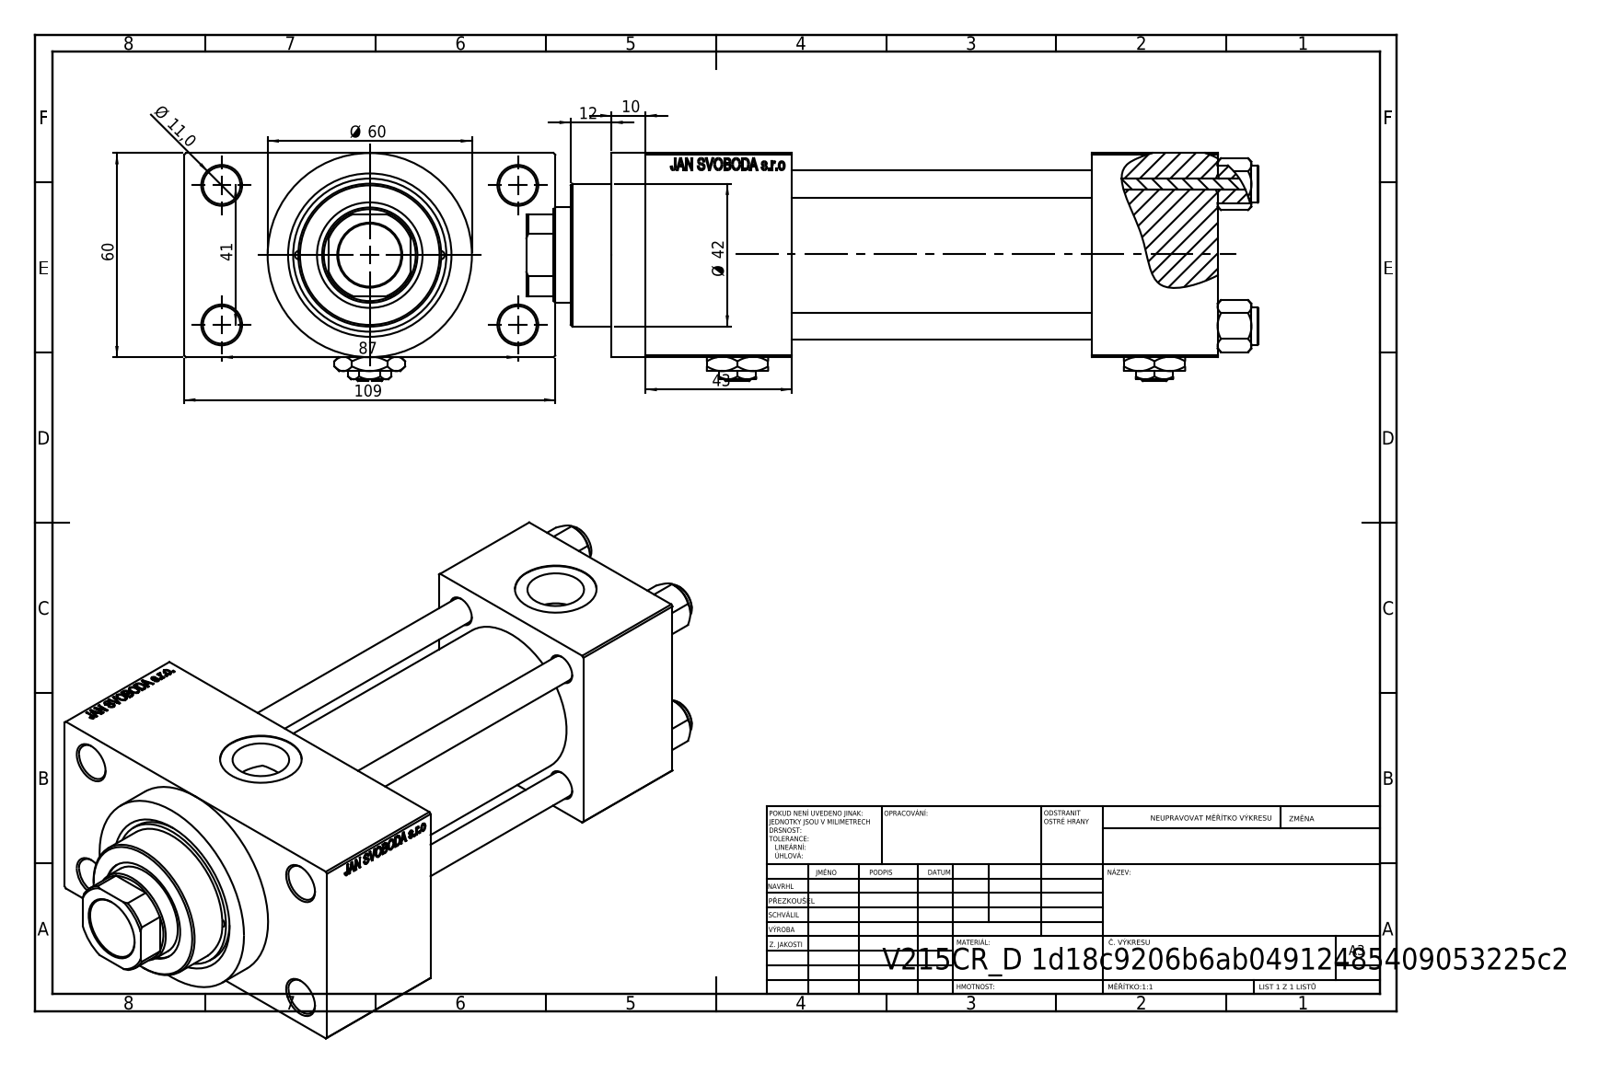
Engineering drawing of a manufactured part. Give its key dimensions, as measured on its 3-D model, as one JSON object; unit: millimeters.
{"part_name": "NUT_M5_D; V215CR_VCP_D; Zatka_pro_OIL_PORT; V215CR_D_Body (+2 more)", "step_written_by": "SolidWorks 2019 (CONFIG_CONTROL_DESIGN)", "units": "millimeters", "bodies": {"solids": 13, "faces": 1216, "planar": 550, "cylindrical": 104, "other": 562}, "overall_size": [215, 109, 67], "volume_mm3": 568397, "surface_area_mm2": 144204, "round_holes": [[8, 4], [11, 4], [2.5, 2], [7, 2], [16.66, 2], [24, 2], [18.5, 1], [28, 1], [31, 1], [40, 1], [45, 1]], "round_bosses_or_shafts": [[11, 4], [60, 1], [46, 1], [42, 1]], "partial_cylinders_radius": [[13.5, 1]], "face_to_face_distances": [60, 24.5, 84.5, 88, 37, 125, 168, 131, 43, 109], "hole_center_spacings": [20.85, 22.65, 29.49, 30.62, 41.7, 46.53, 47.15, 48.09]}
